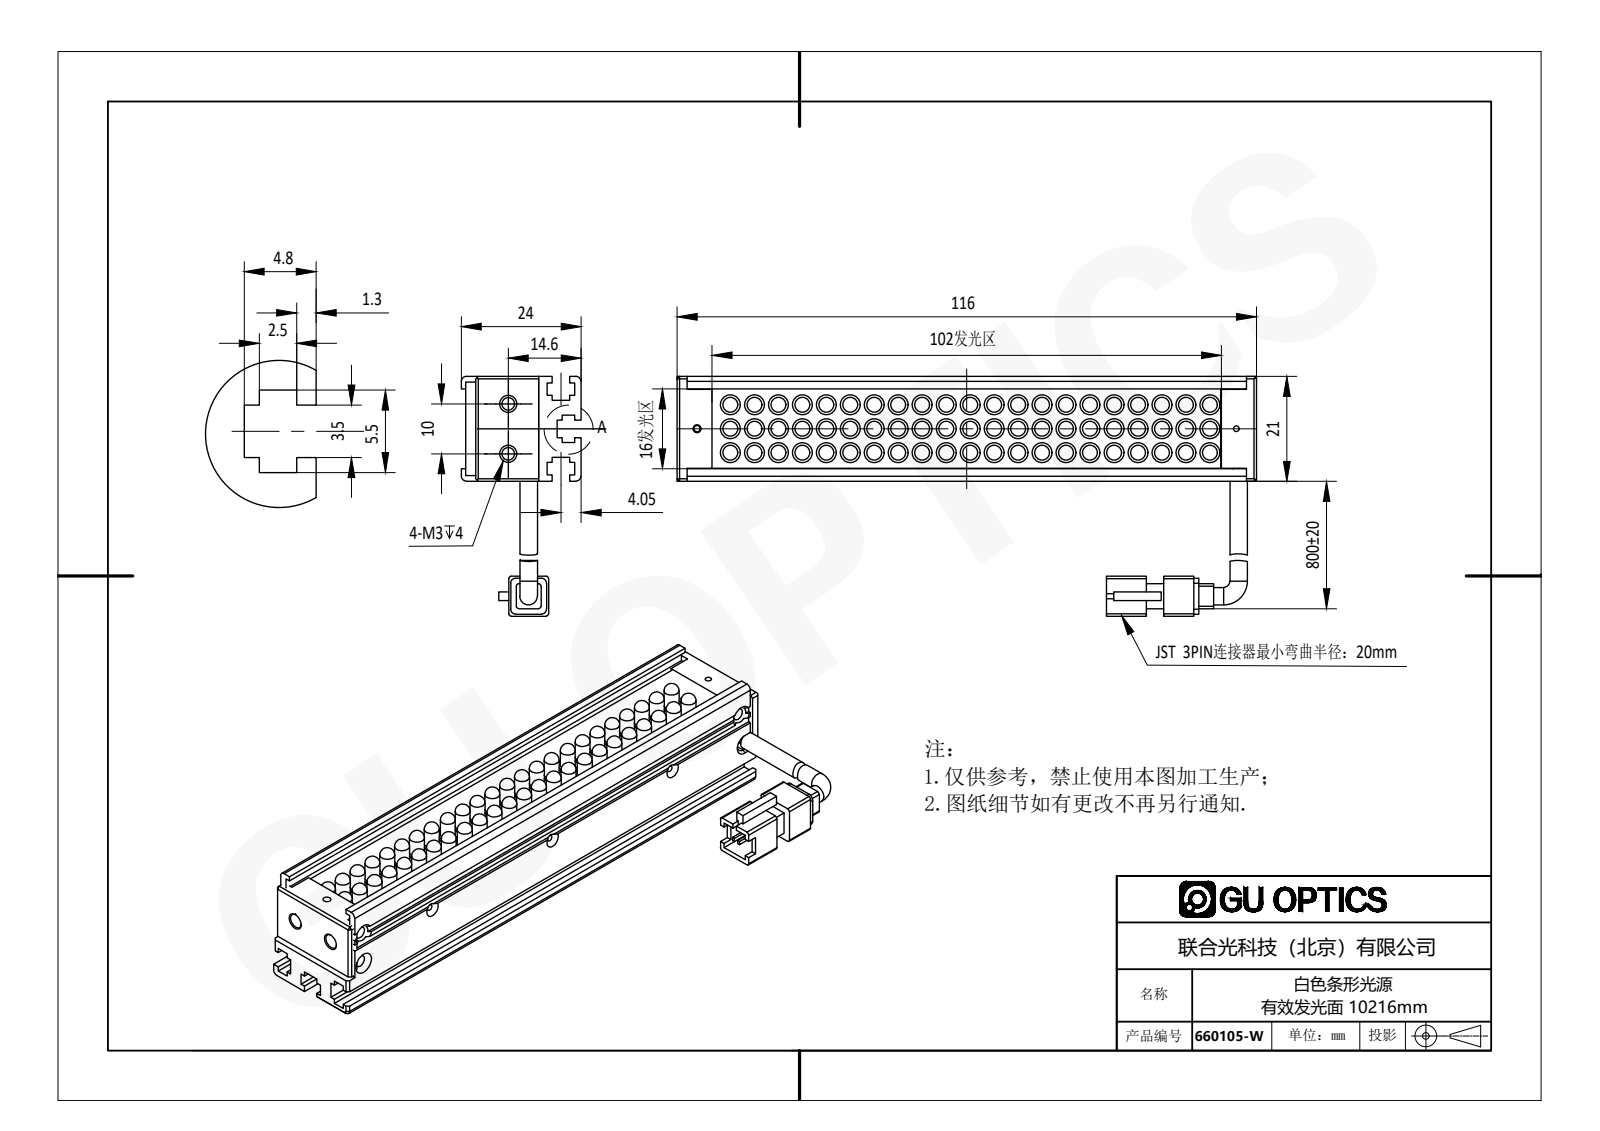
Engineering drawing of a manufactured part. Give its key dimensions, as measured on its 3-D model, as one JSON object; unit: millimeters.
{"part_name": "660105-W", "step_written_by": "SolidWorks 2016 (AUTOMOTIVE_DESIGN)", "units": "millimeters", "bodies": {"solids": 8, "faces": 1630, "planar": 1038, "cylindrical": 395, "other": 197}, "overall_size": [116.99, 48, 24], "volume_mm3": 29929, "surface_area_mm2": 30887, "round_holes": [[1.25, 5], [1.6, 5], [2.4, 4], [2.5, 2], [3, 2]], "round_bosses_or_shafts": [[4, 72], [3, 72], [3.5, 2]], "partial_cylinders_radius": [[0.99, 12], [1, 12], [0.5, 8], [1.65, 1]], "face_to_face_distances": [1, 2.5, 18.5, 3.5, 2.3, 1.3, 6.25, 21, 8.5, 2], "hole_center_spacings": [1.02, 7, 19.81, 53.61, 87.57, 107, 107.23, 6.82]}
